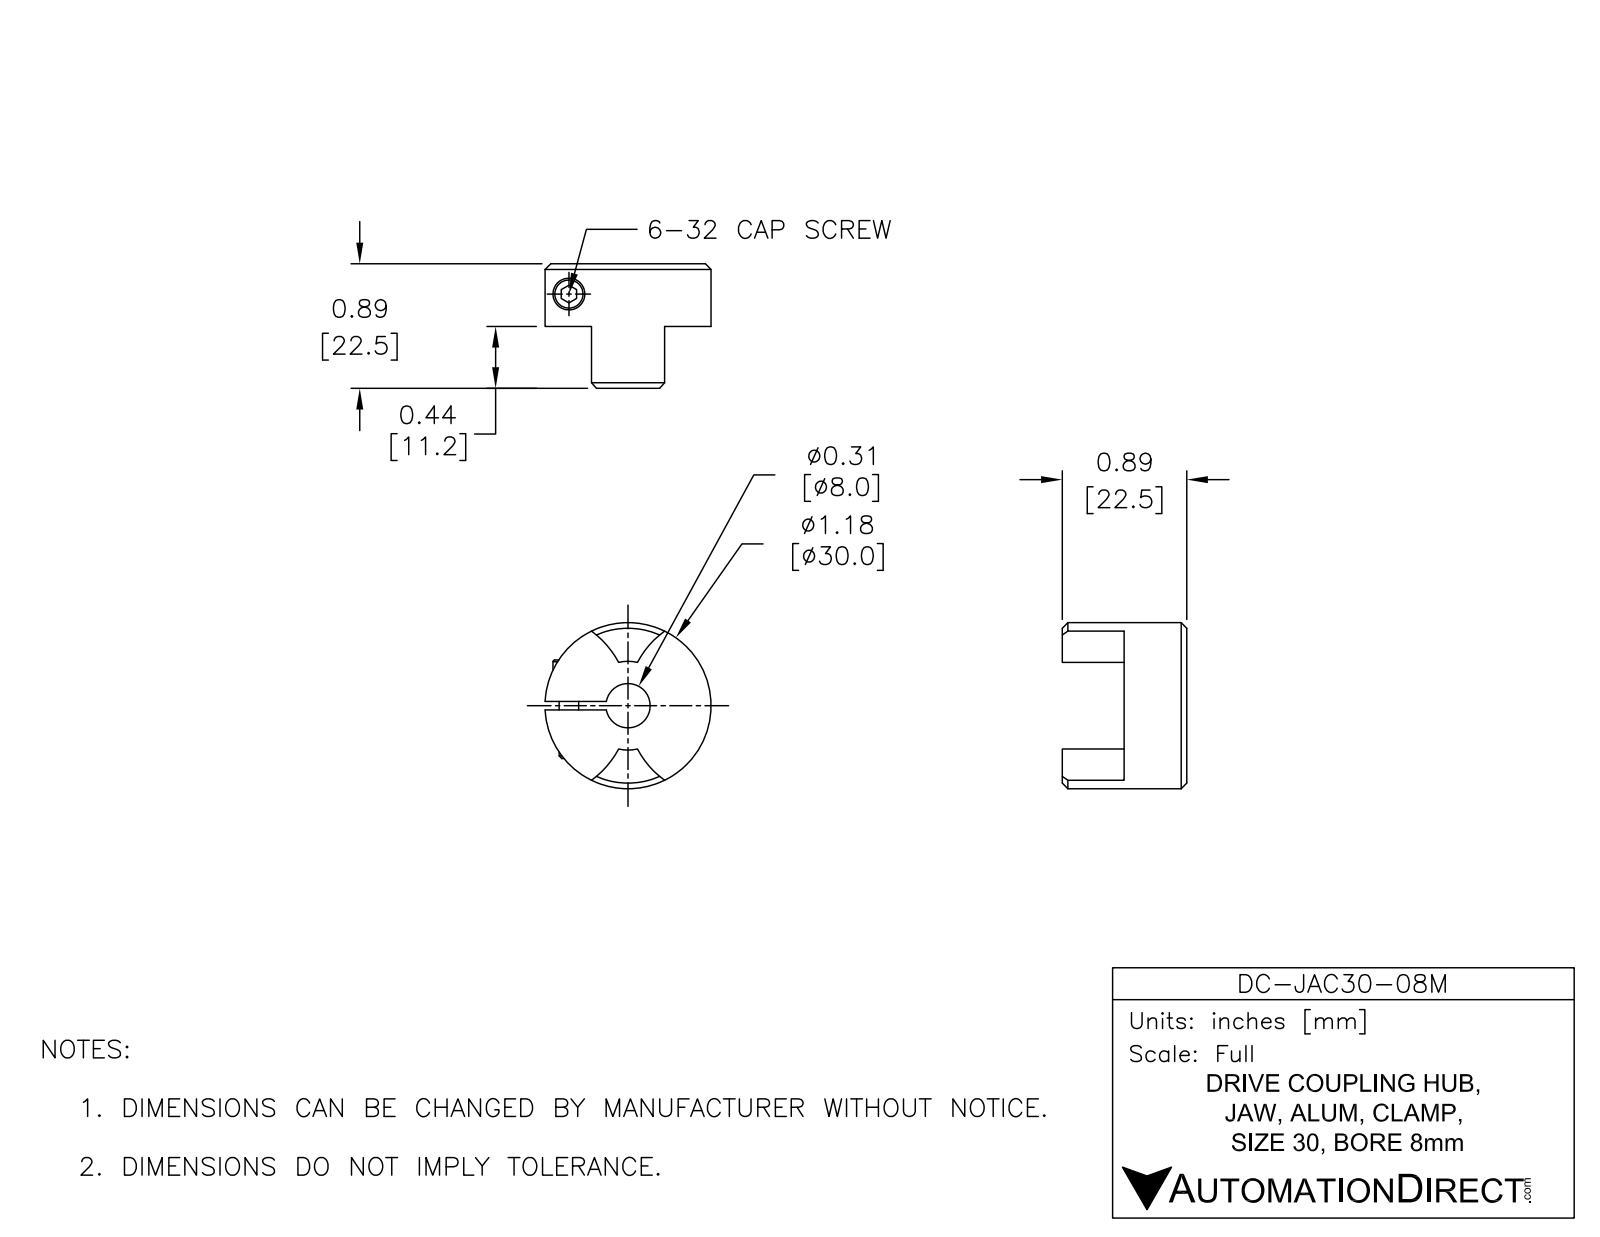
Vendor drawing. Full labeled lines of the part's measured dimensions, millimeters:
Part name (STEP PRODUCT): DC-JAC30-08M
STEP written by: SolidWorks 2015 (AUTOMOTIVE_DESIGN)
Units: millimetres
Bodies: 1 solid, 27 faces (7 planar, 16 cylindrical, 4 other)
Overall size (bounding box): 29.97 × 29.95 × 22.48
Volume: 8 063 mm³ · Surface area: 3 683 mm²
Round holes (diameter × count): ⌀3.91 ×1, ⌀6.35 ×1, ⌀8 ×1
Round bosses / shafts (diameter × count): ⌀29.97 ×1
Partial cylindrical surfaces — rounded edges, fillets, slot ends (radius × count): R16.64 ×2, R8 ×1
Main face-to-face distances: 11.3, 1.52, 22.48, 11.18, 5.51, 3.99
